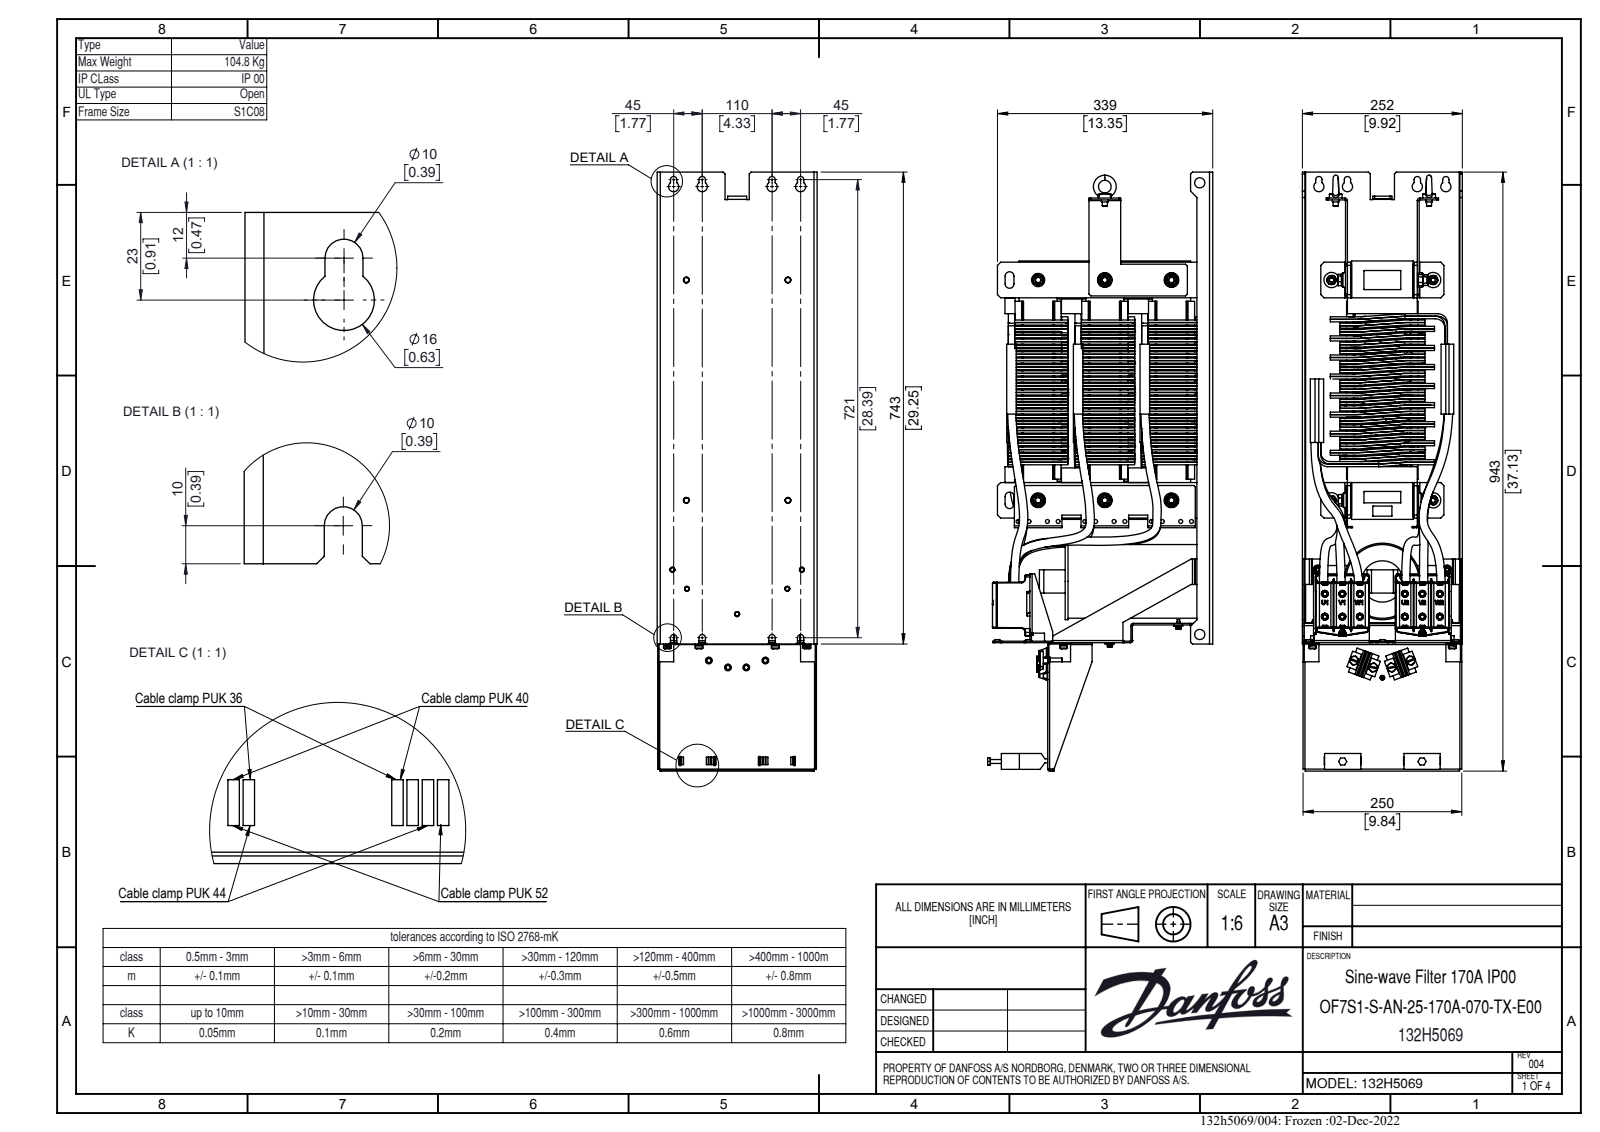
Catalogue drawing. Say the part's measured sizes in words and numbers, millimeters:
The part is named "132H5069-V002-220222_OUT". Its 3-D file was written by "CREO PARAMETRIC BY PTC INC, 2020342 (CONFIG_CONTROL_DESIGN)". It is 3 solids with 2337 faces: 1423 planar, 667 cylindrical and 247 other. Overall it measures 943 by 354.5 by 252 millimeters. Its volume is 18 650 000 cubic millimeters and its surface area 1 883 000 square millimeters. Round holes: 12 of diameter 6.2, 9 of diameter 10.02, 5 of diameter 7, 4 of diameter 5, 4 of diameter 8.4, 4 of diameter 9, 4 of diameter 18.78, 2 of diameter 6.8, 2 of diameter 10, 2 of diameter 16, 2 of diameter 19.12, 1 of diameter 7.15. Round bosses or shafts: 17 of diameter 6, 14 of diameter 8, 8 of diameter 20, 7 of diameter 7, 6 of diameter 23, 6 of diameter 5, 5 of diameter 10, 4 of diameter 24. Partial cylindrical surfaces (rounded edges, fillets, slot ends): 40 of radius 1, 28 of radius 3, 24 of radius 0.5, 20 of radius 3.5, 12 of radius 7.5, 11 of radius 5, 8 of radius 3.6, 8 of radius 4.5. The main face-to-face distances are 4, 2, 105, 245, 3, 68, 180, 181, 1, 65. The hole center spacings are 105, 45.36, 17, 36, 46, 27.6, 59, 88.
